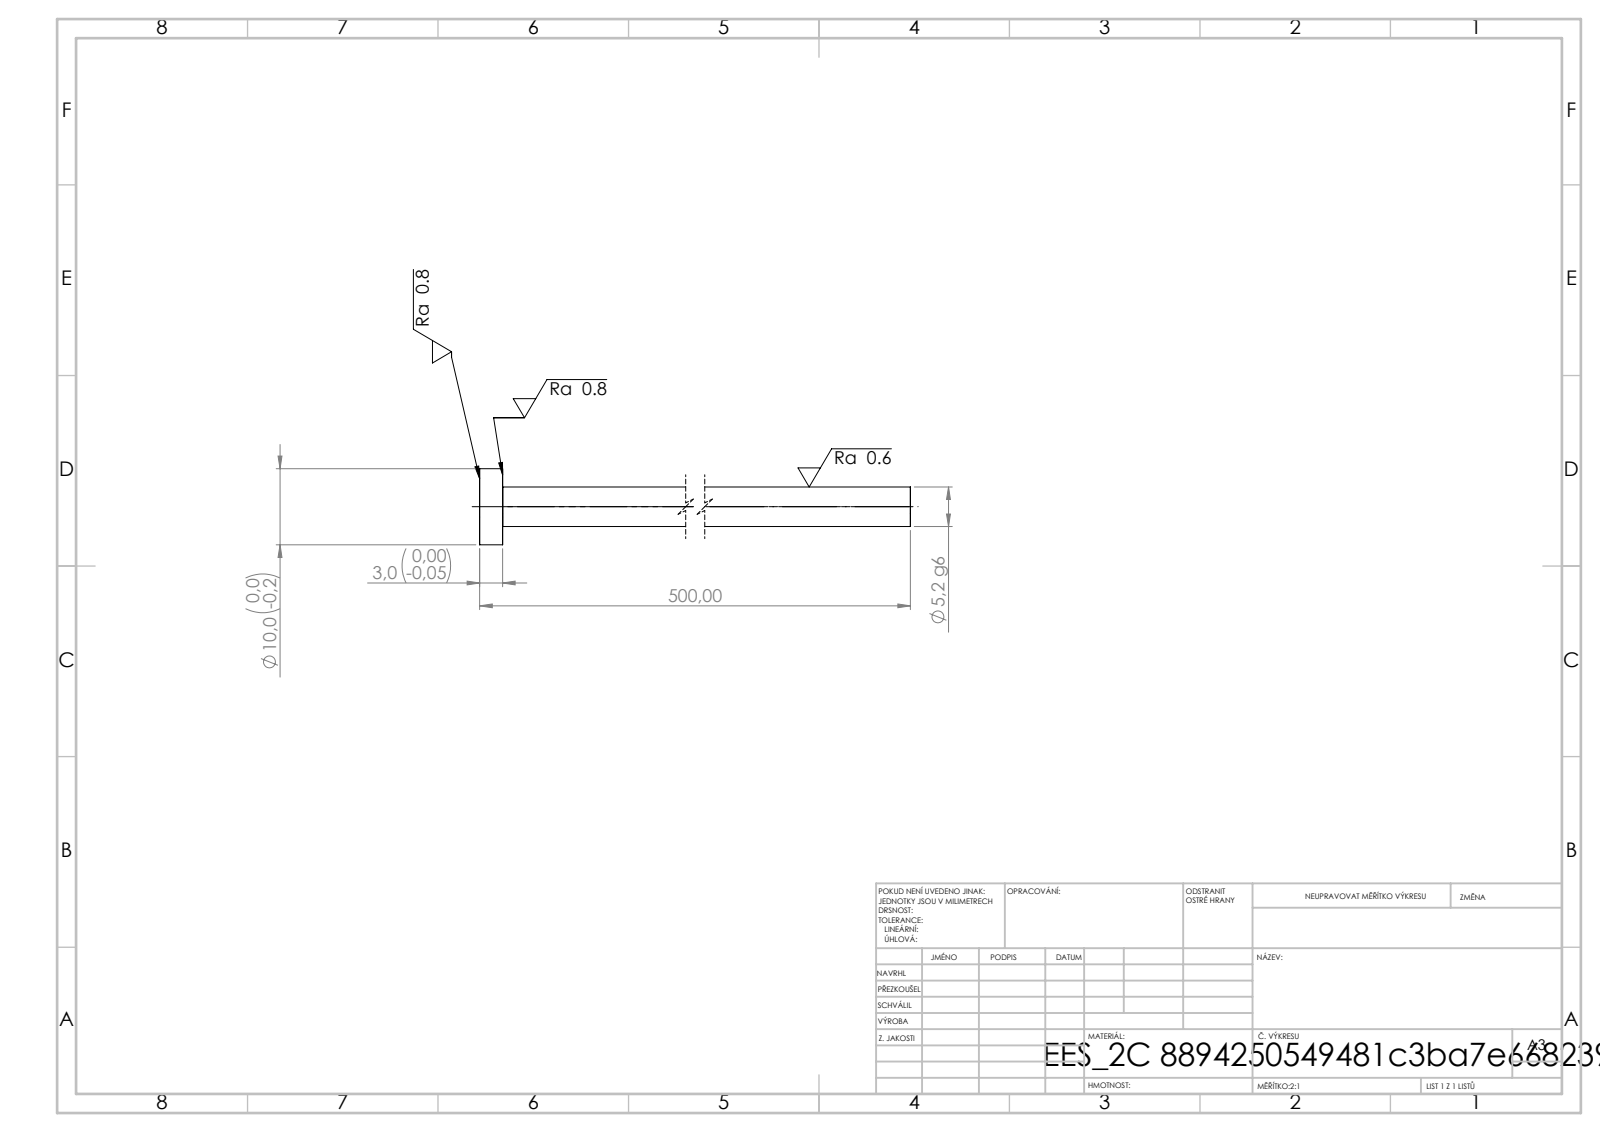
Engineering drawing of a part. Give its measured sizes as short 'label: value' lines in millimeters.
written by: SolidWorks 2019 (CONFIG_CONTROL_DESIGN)
unit: mm
bodies: 1 solid, 7 faces (3 planar, 4 cylindrical, 0 other)
size: 500 × 10 × 10
volume: 10 790 mm³; area: 8 370 mm²
bosses: 1× ⌀10, 1× ⌀5.2
face distances: 3, 500, 497
